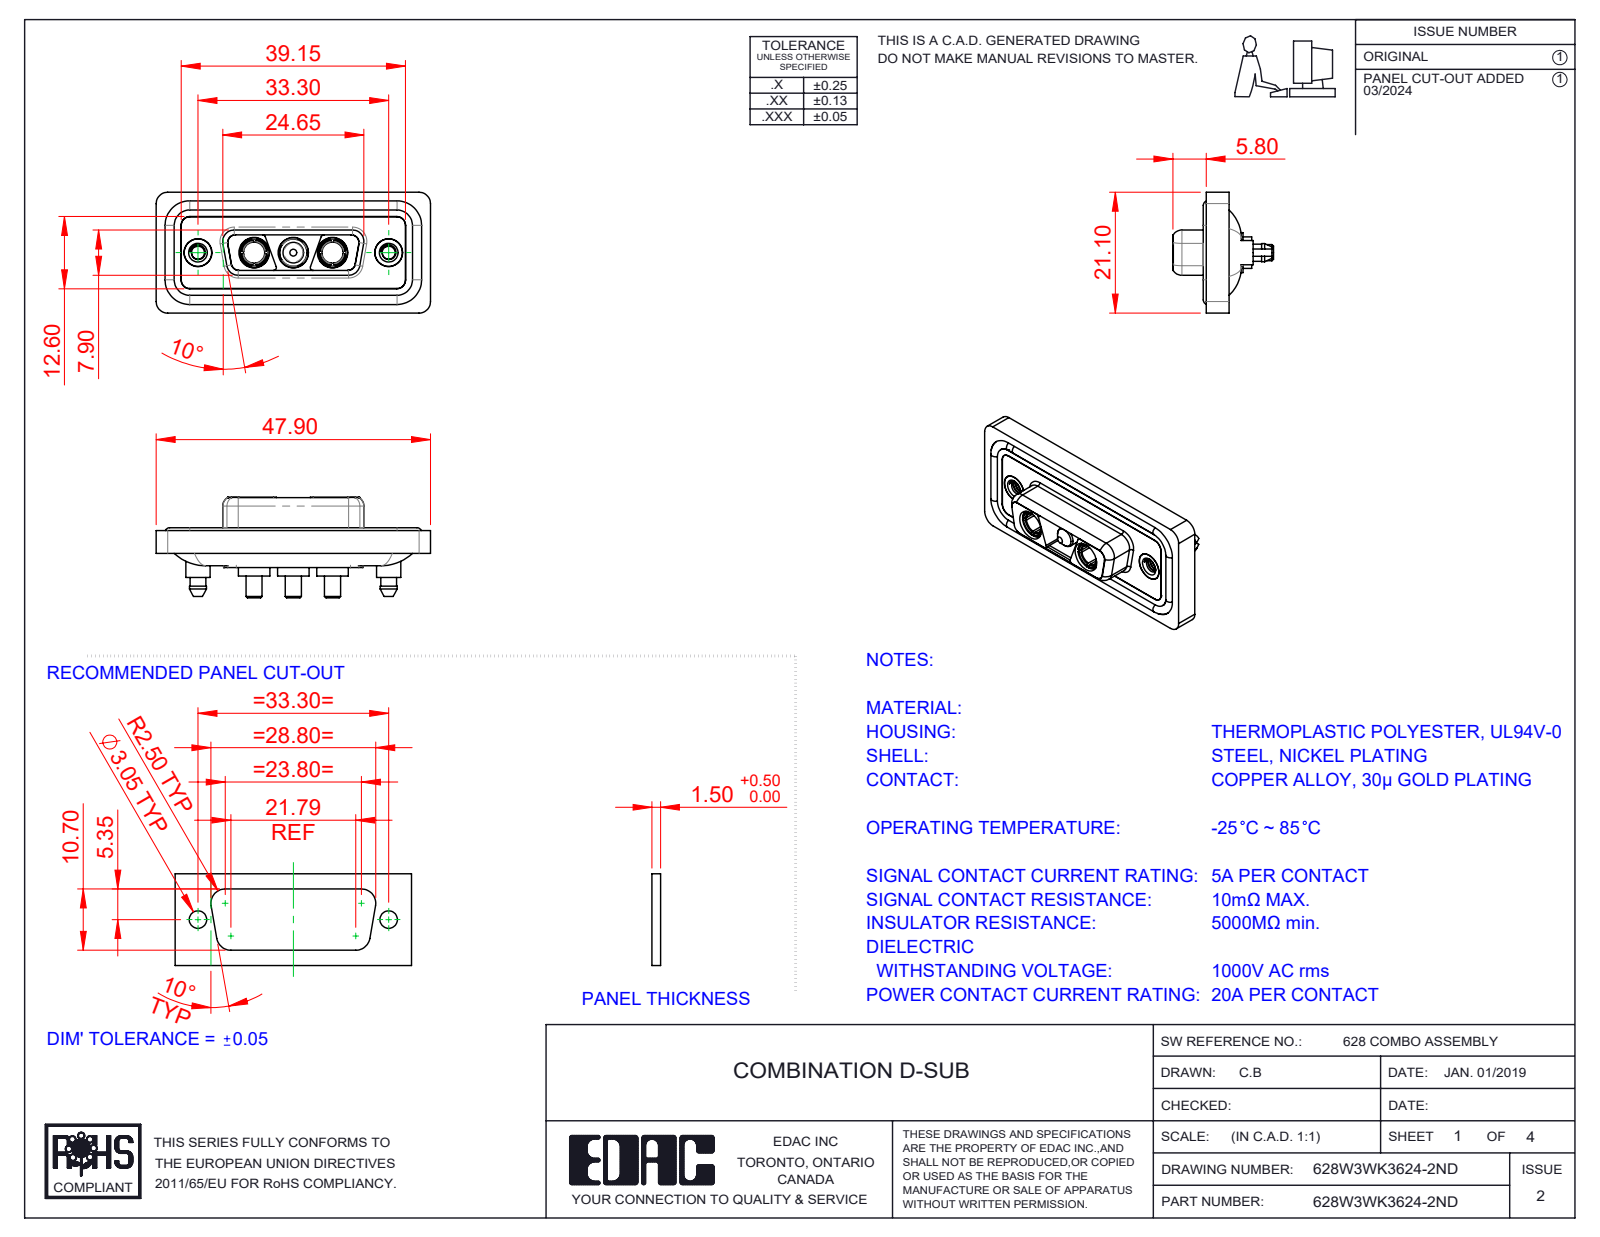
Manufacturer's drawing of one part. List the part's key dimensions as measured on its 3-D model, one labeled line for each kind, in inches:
Part name (STEP PRODUCT): 628W3WK3624-2ND; Power Pin_20A S; Power Socket_20A S; 628Combo Shell Front_15 Contacts (+4 more)
STEP written by: SolidWorks 2023 (CONFIG_CONTROL_DESIGN)
Units: inches
Bodies: 13 solids, 649 faces (194 planar, 306 cylindrical, 149 other)
Overall size (bounding box): 1.886 × 0.831 × 0.691
Volume: 0.367 in³ · Surface area: 15.26 in²
Round holes (diameter × count): ⌀0.191 ×5, ⌀0.209 ×3, ⌀0.089 ×2, ⌀0.146 ×2, ⌀0.157 ×2, ⌀0.159 ×2, ⌀0.197 ×2
Round bosses / shafts (diameter × count): ⌀0.063 ×4, ⌀0.217 ×3, ⌀0.205 ×3, ⌀0.187 ×3, ⌀0.148 ×3, ⌀0.11 ×3, ⌀0.213 ×2, ⌀0.195 ×2
Partial cylindrical surfaces — rounded edges, fillets, slot ends (radius × count): R0.059 ×24, R0.079 ×20, R0.053 ×12, R0.063 ×10, R0.02 ×8, R0.01 ×4, R0.024 ×4, R0.026 ×4
Main face-to-face distances: 0.016, 0.063, 0.071, 0.02, 0.043, 0.114, 0.222, 0.278, 0.059, 0.211
Hole centre spacings: 0.27, 0.386, 0.656, 0.925, 0.539, 1.311
